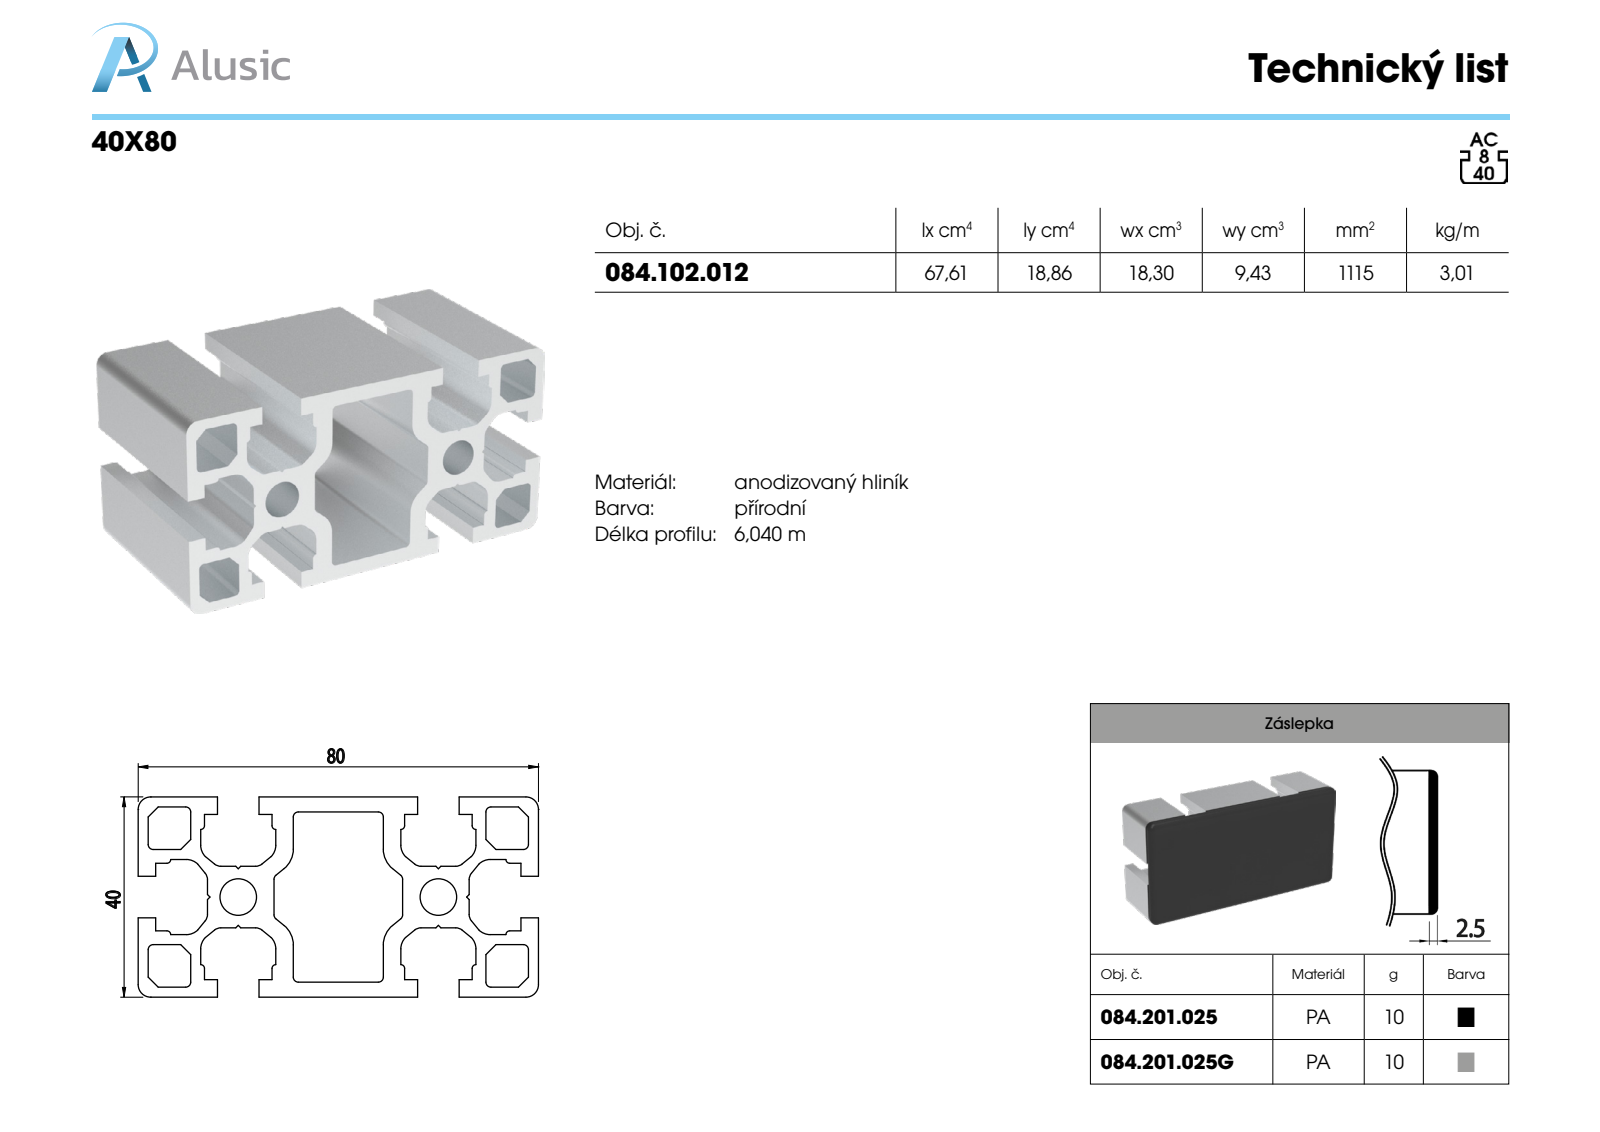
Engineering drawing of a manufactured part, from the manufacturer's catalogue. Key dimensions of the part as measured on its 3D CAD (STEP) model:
Part name (STEP PRODUCT): 084.102.012
STEP written by: SolidWorks 2012 (CONFIG_CONTROL_DESIGN)
Units: millimetres
Bodies: 1 solid, 196 faces (132 planar, 64 cylindrical, 0 other)
Overall size (bounding box): 80 × 50 × 40
Volume: 55 746 mm³ · Surface area: 38 939 mm²
Round holes (diameter × count): ⌀7.3 ×2
Partial cylindrical surfaces — rounded edges, fillets, slot ends (radius × count): R1 ×16, R0.75 ×12, R2 ×12, R3.2 ×12, R2.5 ×4, R5 ×4
Main face-to-face distances: 2, 40, 3.35, 10.5, 13.85, 13.65, 24.15, 27.5, 37, 3
Hole centre spacings: 40
